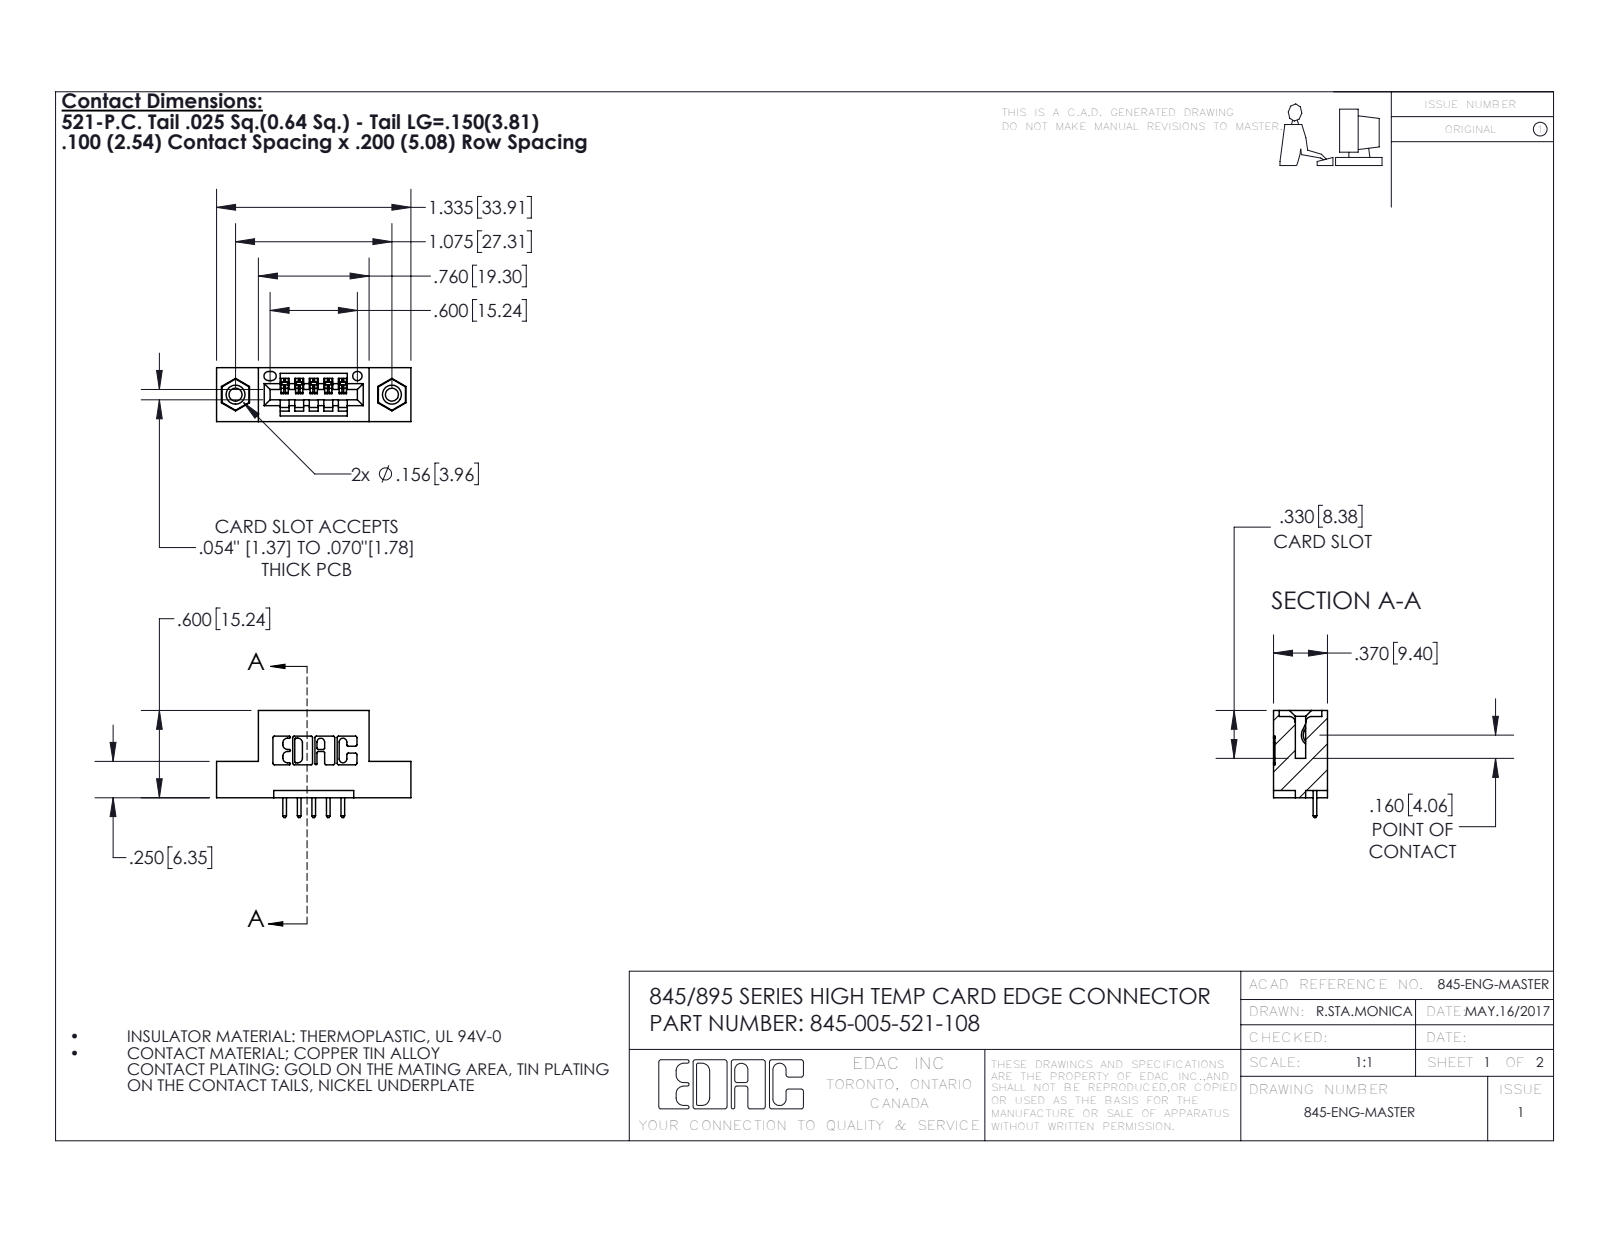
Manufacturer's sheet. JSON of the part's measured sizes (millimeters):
{"part_name": "345-250-001_345-250-003-102; 345 Part_Flush Mounting Lugs - 0.156 Dia-TI; 345-292-001_345-293-121; 345-005-521-108", "step_written_by": "SolidWorks 2016 (CONFIG_CONTROL_DESIGN)", "units": "millimeters", "bodies": {"solids": 8, "faces": 476, "planar": 312, "cylindrical": 148, "other": 16}, "overall_size": [33.9, 18.7, 9.4], "volume_mm3": 2900, "surface_area_mm2": 3310, "round_holes": [[2.3, 2], [3.2, 2], [4, 2], [1.6, 1]], "round_bosses_or_shafts": [[3.9, 2]], "partial_cylinders_radius": [[0.3, 22], [0.2, 10], [0.3, 10], [0.2, 6], [0.8, 6], [0.7, 3], [0.8, 2], [1, 2]], "face_to_face_distances": [5.1, 9.4, 1.8, 7.6, 2.5, 0.6, 8.9, 6.4, 2.5, 6.9], "hole_center_spacings": [6.9, 21.5, 27.3]}
